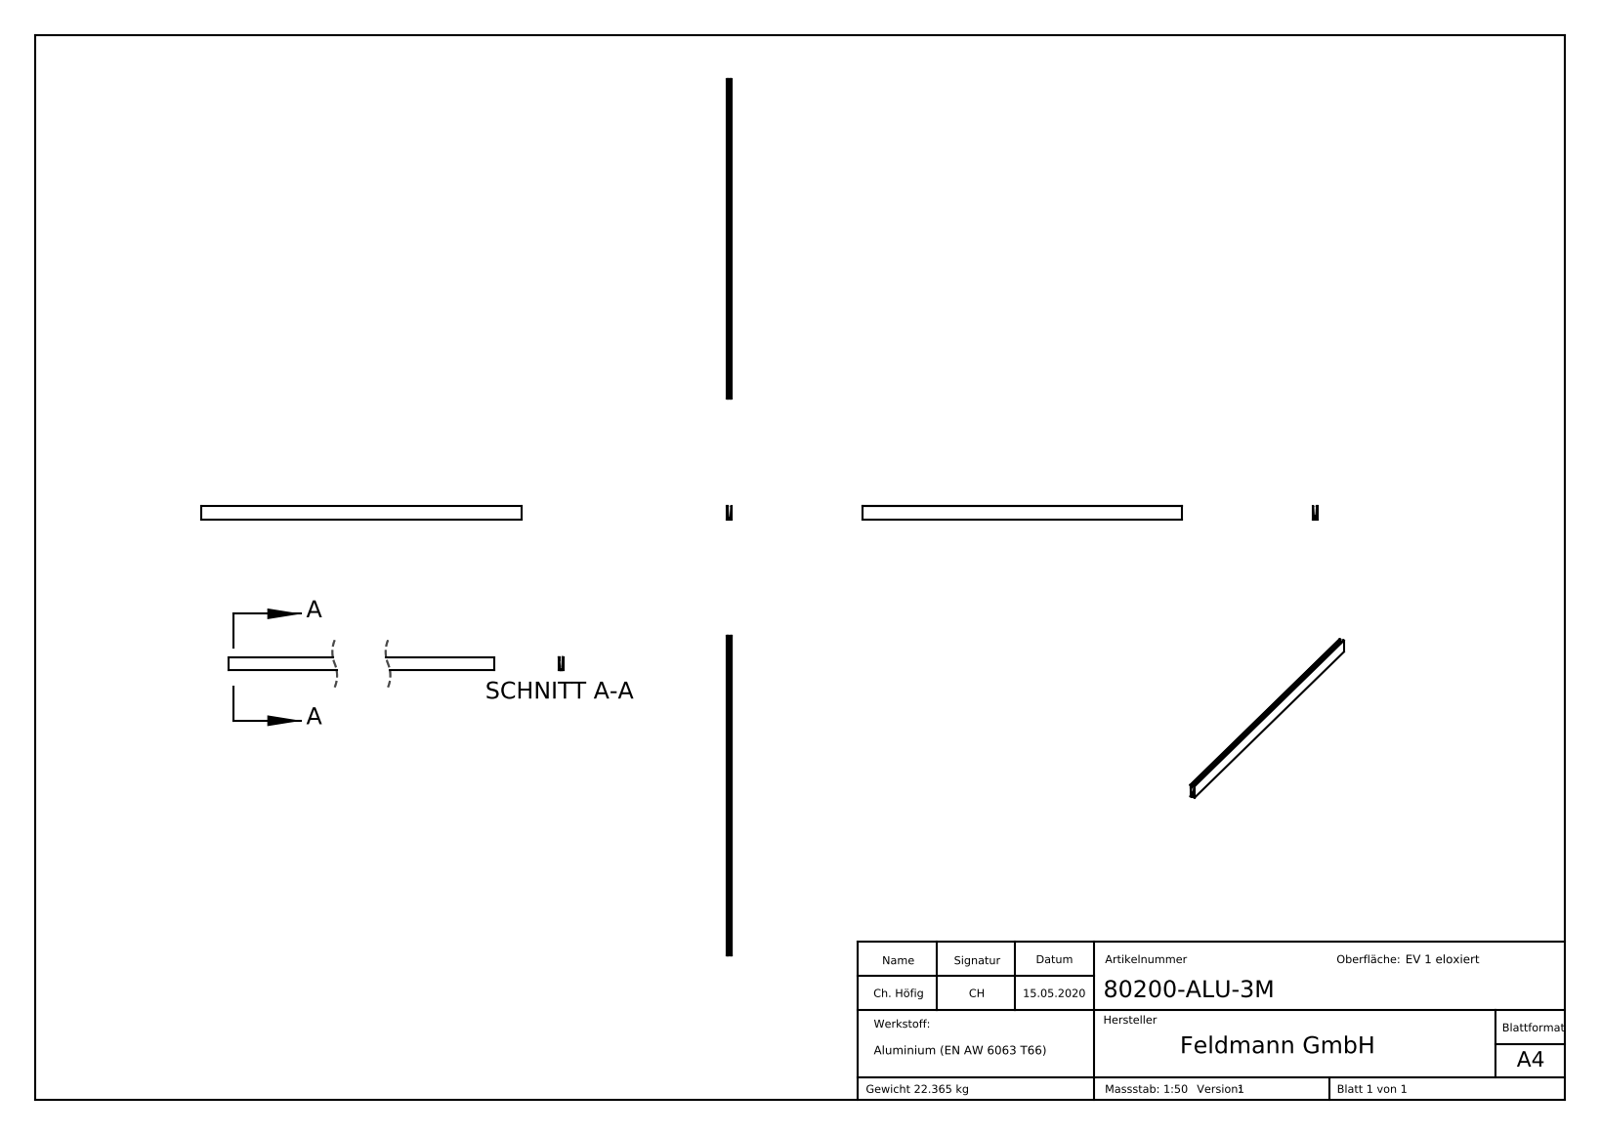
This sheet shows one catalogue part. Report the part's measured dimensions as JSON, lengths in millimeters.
{"part_name": "80200-ALU-3M", "step_written_by": "SolidWorks 2015 (CONFIG_CONTROL_DESIGN)", "units": "millimeters", "bodies": {"solids": 1, "faces": 494, "planar": 184, "cylindrical": 131, "other": 179}, "overall_size": [3000, 125, 47], "volume_mm3": 8283000, "surface_area_mm2": 1689000, "round_holes": [[13, 30]], "partial_cylinders_radius": [[11.2, 30], [0.5, 4], [1, 3], [0.65, 2], [0.25, 1]], "face_to_face_distances": [47, 12, 35, 7.94, 39.06, 4.06, 27.06, 23, 3, 15], "hole_center_spacings": [100, 200, 300, 400, 500, 600, 700, 800]}
